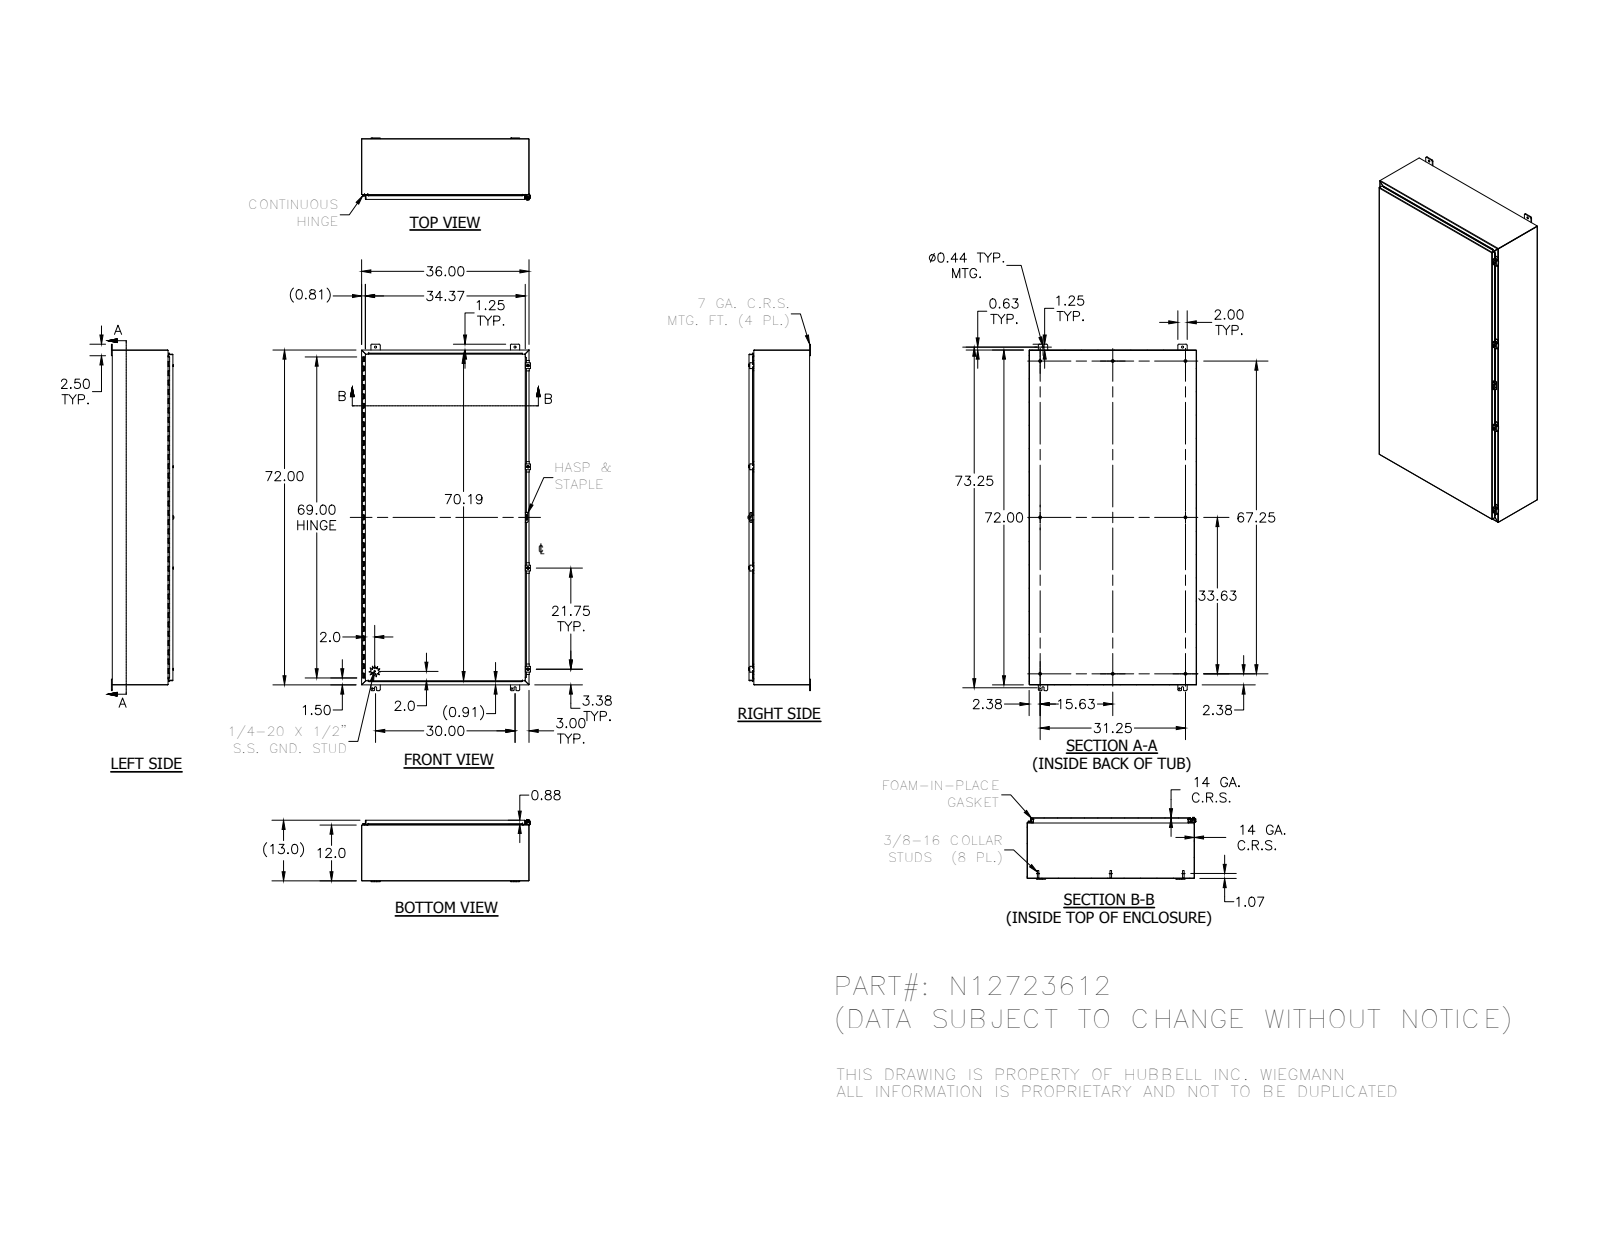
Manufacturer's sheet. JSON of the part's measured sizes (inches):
{"part_name": "N12723612; 34840; 38413; N123612TB (+8 more)", "step_written_by": "Autodesk Inventor 2012 (AUTOMOTIVE_DESIGN)", "units": "inches", "bodies": {"solids": 43, "faces": 1580, "planar": 935, "cylindrical": 502, "other": 143}, "overall_size": [74.5, 36.311, 13.41], "volume_in3": 647.3, "surface_area_in2": 17208, "round_holes": [[0.211, 4], [0.281, 4], [0.3, 4], [0.313, 4], [0.438, 4], [0.11, 3], [0.125, 1], [0.156, 1], [0.5, 1]], "round_bosses_or_shafts": [[0.625, 8], [0.33, 8], [0.25, 6], [0.52, 4], [0.5, 4], [0.35, 4], [0.337, 1], [0.12, 1]], "partial_cylinders_radius": [[0.03, 51], [0.125, 29], [0.25, 29], [0.031, 21], [0.105, 21], [0.063, 17], [0.1, 8], [0.141, 8]], "face_to_face_distances": [0.074, 12.959, 12.885, 13.033, 35.926, 71.926, 36, 35.852, 11.926, 1.033], "hole_center_spacings": [1.593, 30, 72, 78, 21.75, 0.791, 29.348, 30.72]}
